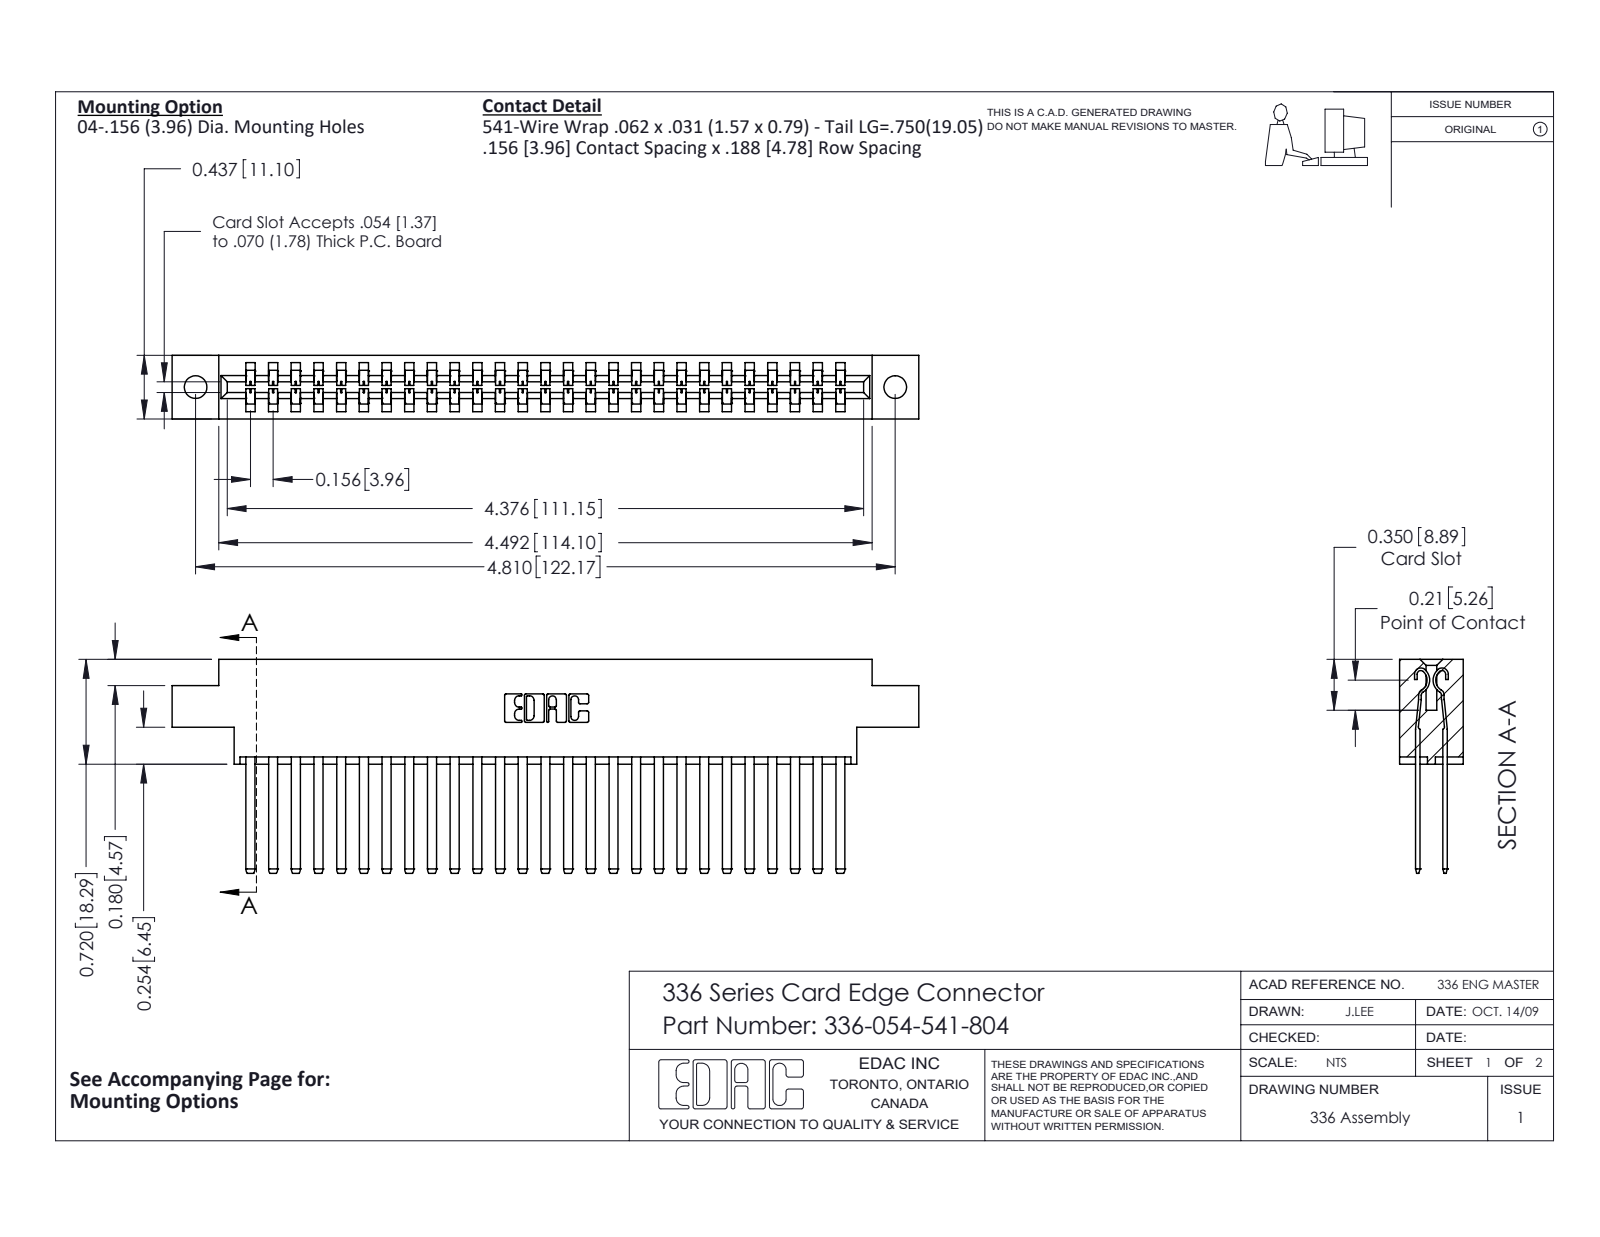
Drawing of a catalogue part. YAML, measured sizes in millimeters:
part_name: "336-290-001_336-290-541; 336-054-541-804; 336 Part_Offset - .156 Dia - TH"
step_written_by: "SolidWorks 2020 (CONFIG_CONTROL_DESIGN)"
units: millimeters
bodies: {solids: 55, faces: 2386, planar: 1478, cylindrical: 908, other: 0}
overall_size: [130.4, 37.3, 11.1]
volume: 19570
surface_area: 24630
round_holes:
  - {diameter: 4, count: 2}
partial_cylinders:
  - {radius: 0.1, count: 108}
  - {radius: 1.4, count: 54}
  - {radius: 0.3, count: 22}
  - {radius: 0.2, count: 6}
  - {radius: 0.8, count: 6}
  - {radius: 0.6, count: 4}
  - {radius: 1, count: 4}
  - {radius: 0.7, count: 3}
face_to_face_distances: [4.8, 8.3, 3.6, 7.5, 2.8, 0.8, 11.1, 0.8, 4.6, 6.5]
hole_center_spacings: [122.2]
